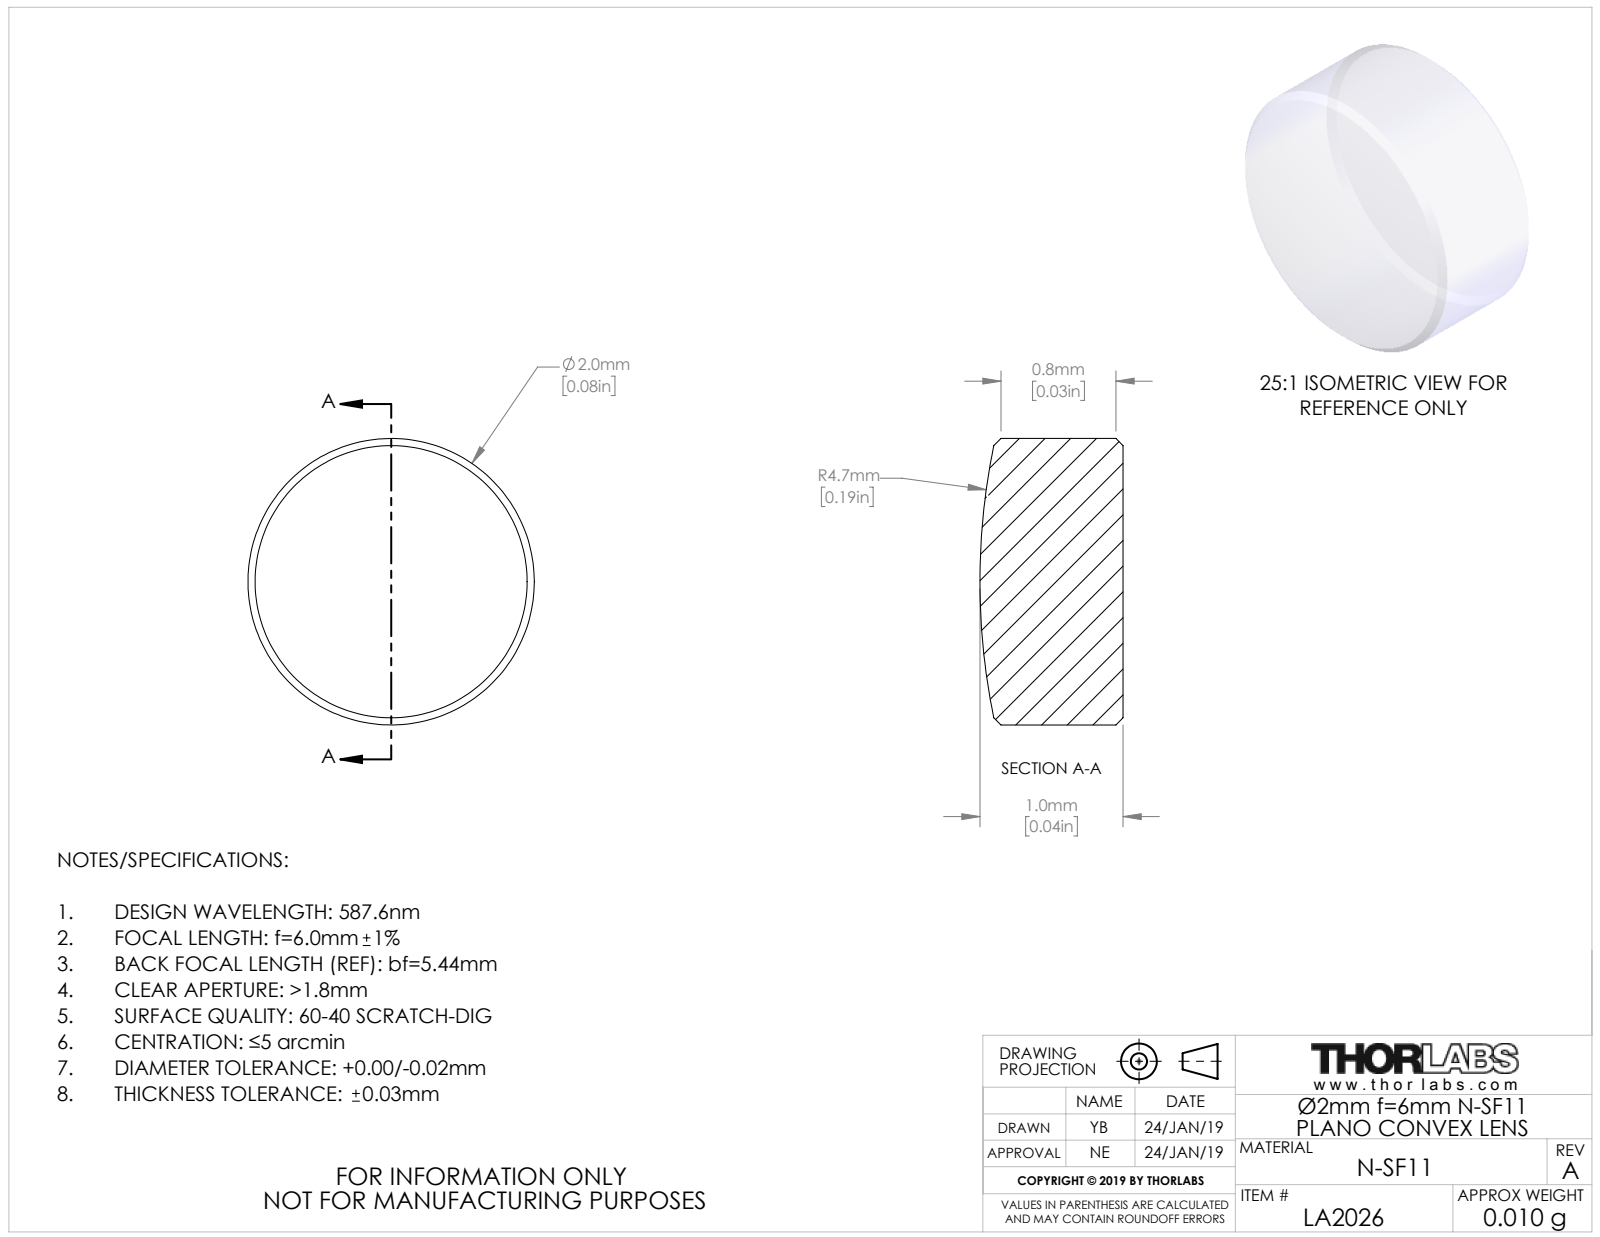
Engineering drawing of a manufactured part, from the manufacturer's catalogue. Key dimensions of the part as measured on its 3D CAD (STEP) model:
Part name (STEP PRODUCT): TTN162740-E0W
STEP written by: SolidWorks 2018 (CONFIG_CONTROL_DESIGN)
Units: millimetres
Bodies: 1 solid, 9 faces (1 planar, 2 cylindrical, 6 other)
Overall size (bounding box): 2 × 2 × 1
Volume: 3 mm³ · Surface area: 12 mm²
Round bosses / shafts (diameter × count): ⌀2 ×1
